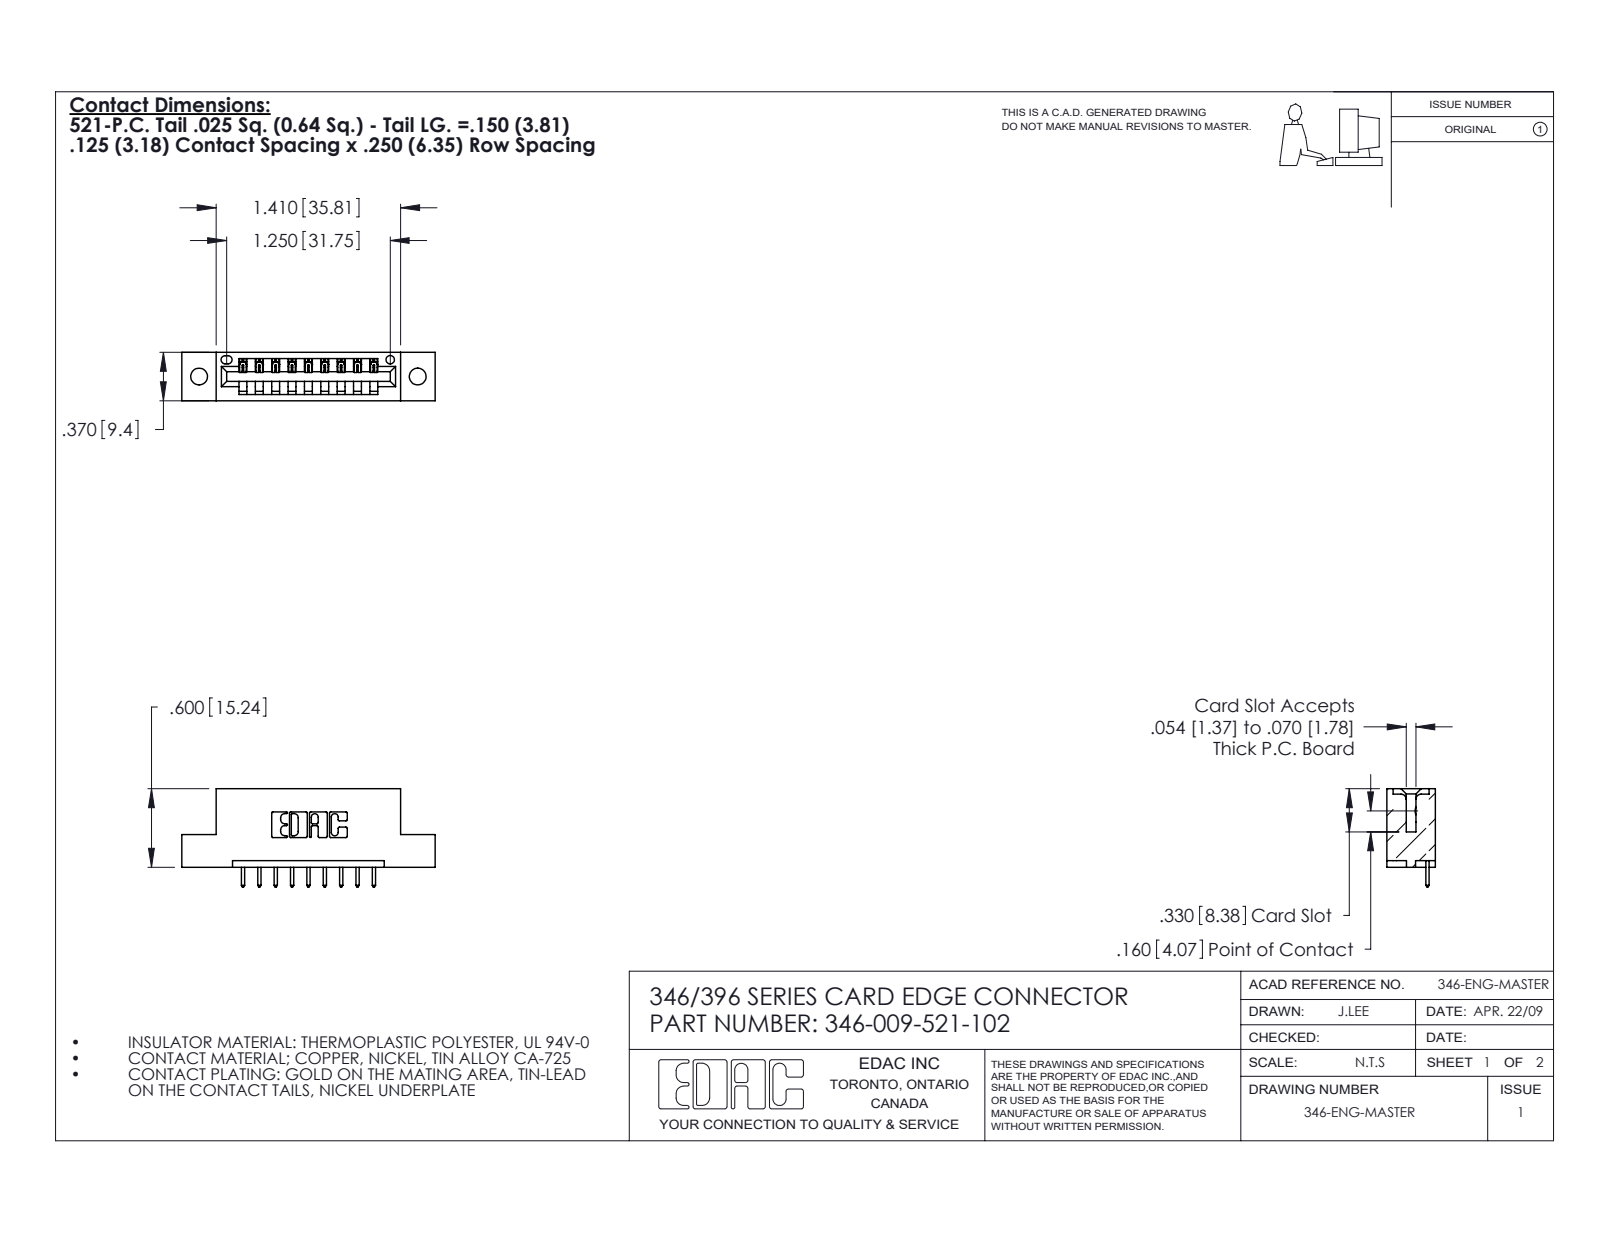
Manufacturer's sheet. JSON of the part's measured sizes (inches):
{"part_name": "346 Part_Flush Mounting Lugs - 0.128 Dia; 345-292-001_345-293-121; 346-009-521-102", "step_written_by": "SolidWorks 2020 (CONFIG_CONTROL_DESIGN)", "units": "inches", "bodies": {"solids": 10, "faces": 644, "planar": 436, "cylindrical": 208, "other": 0}, "overall_size": [1.935, 0.75, 0.37], "volume_in3": 0.269, "surface_area_in2": 7.423, "round_holes": [[0.128, 2], [0.064, 1]], "partial_cylinders_radius": [[0.01, 22], [0.006, 18], [0.01, 18], [0.007, 6], [0.031, 6], [0.026, 3], [0.031, 2], [0.04, 2]], "face_to_face_distances": [0.25, 0.37, 0.048, 0.322, 0.148, 0.222, 0.1, 0.174, 0.072, 0.298], "hole_center_spacings": [0.246, 1.465, 1.67]}
